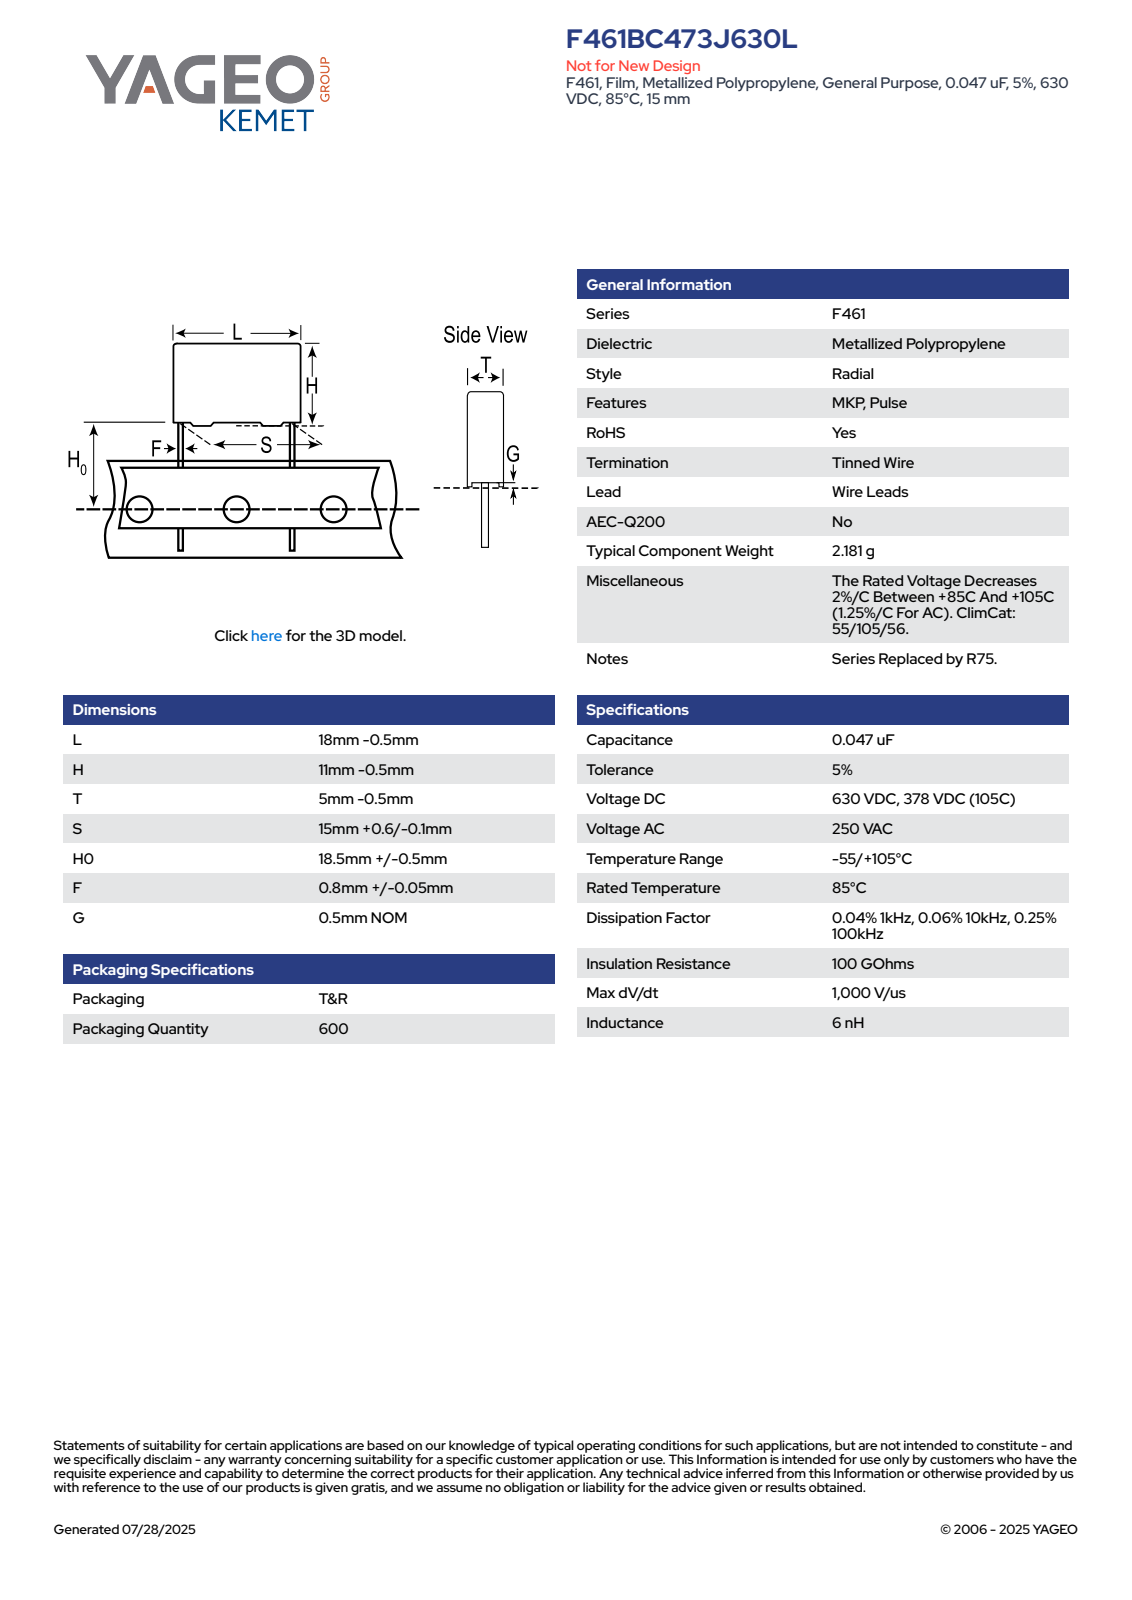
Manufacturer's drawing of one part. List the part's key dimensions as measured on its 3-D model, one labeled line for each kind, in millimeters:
Part name (STEP PRODUCT): CFR_RBG_18X11X5_L17.5H10.5T4.5S15H019F0.85G0.5
STEP written by: SolidWorks 2014 (AUTOMOTIVE_DESIGN)
Units: millimetres
Bodies: 4 solids, 89 faces (81 planar, 8 cylindrical, 0 other)
Overall size (bounding box): 29.5 × 17.5 × 4.5
Volume: 809 mm³ · Surface area: 737 mm²
Round bosses / shafts (diameter × count): ⌀0.85 ×2
Partial cylindrical surfaces — rounded edges, fillets, slot ends (radius × count): R0.5 ×4
Main face-to-face distances: 4.5, 10, 17.5, 4.24, 3.98, 0.5, 10.5, 19, 19.5, 29.5
